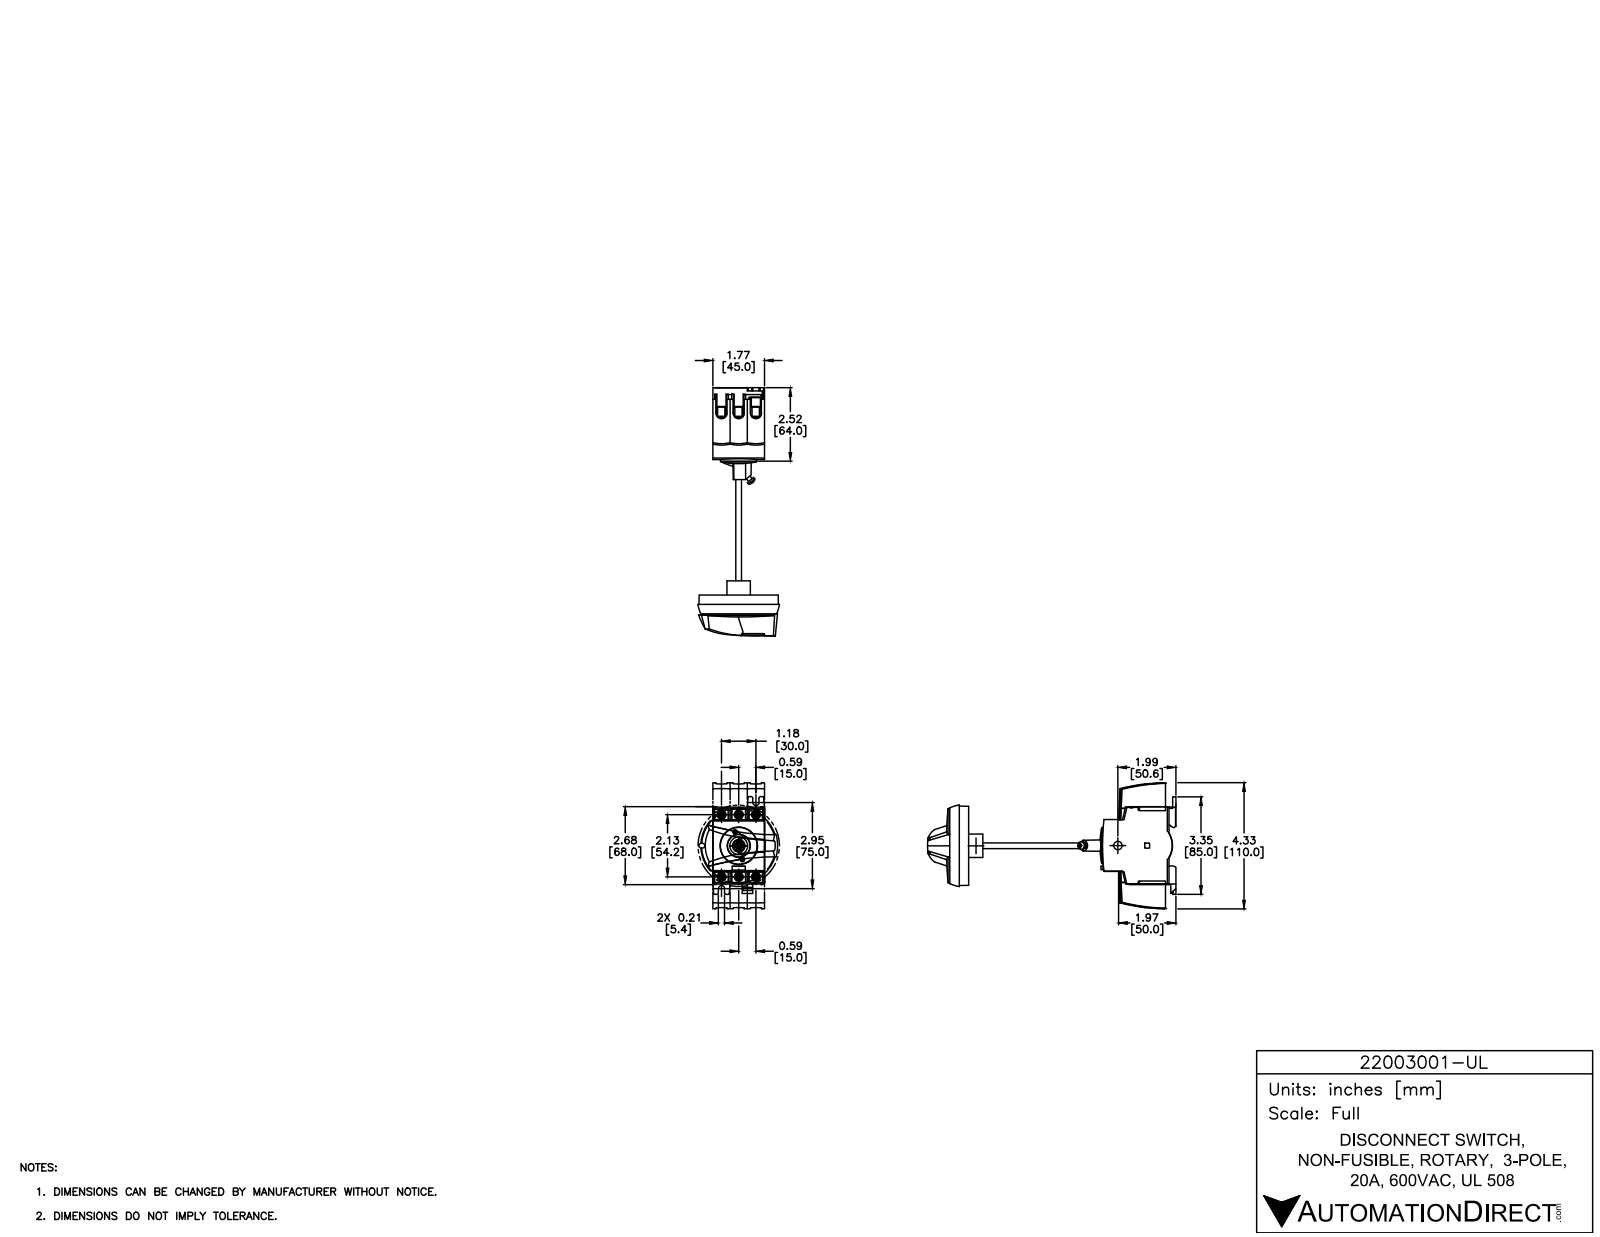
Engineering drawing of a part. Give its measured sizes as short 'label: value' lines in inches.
name: 22003001-UL
written by: SolidWorks 2015 (AUTOMOTIVE_DESIGN)
unit: in
bodies: 1 solid, 463 faces (389 planar, 50 cylindrical, 24 other)
size: 3.346 × 2.571 × 1.772
volume: 9.498 in³; area: 40.23 in²
holes: 6× ⌀0.26, 1× ⌀0.283, 1× ⌀1.244
rounds: 13× R0.012, 5× R0.02, 4× R0.165, 3× R0.039, 2× R0.106, 1× R0.13, 1× R0.354, 1× R0.37
face distances: 1.772, 0.433, 2.205, 2.157, 2.638, 2.28, 0.591, 2.591, 0.047, 0.386
hole spacings: 0.591, 1.219, 2.214, 2.134, 1.067, 1.181, 2.439
